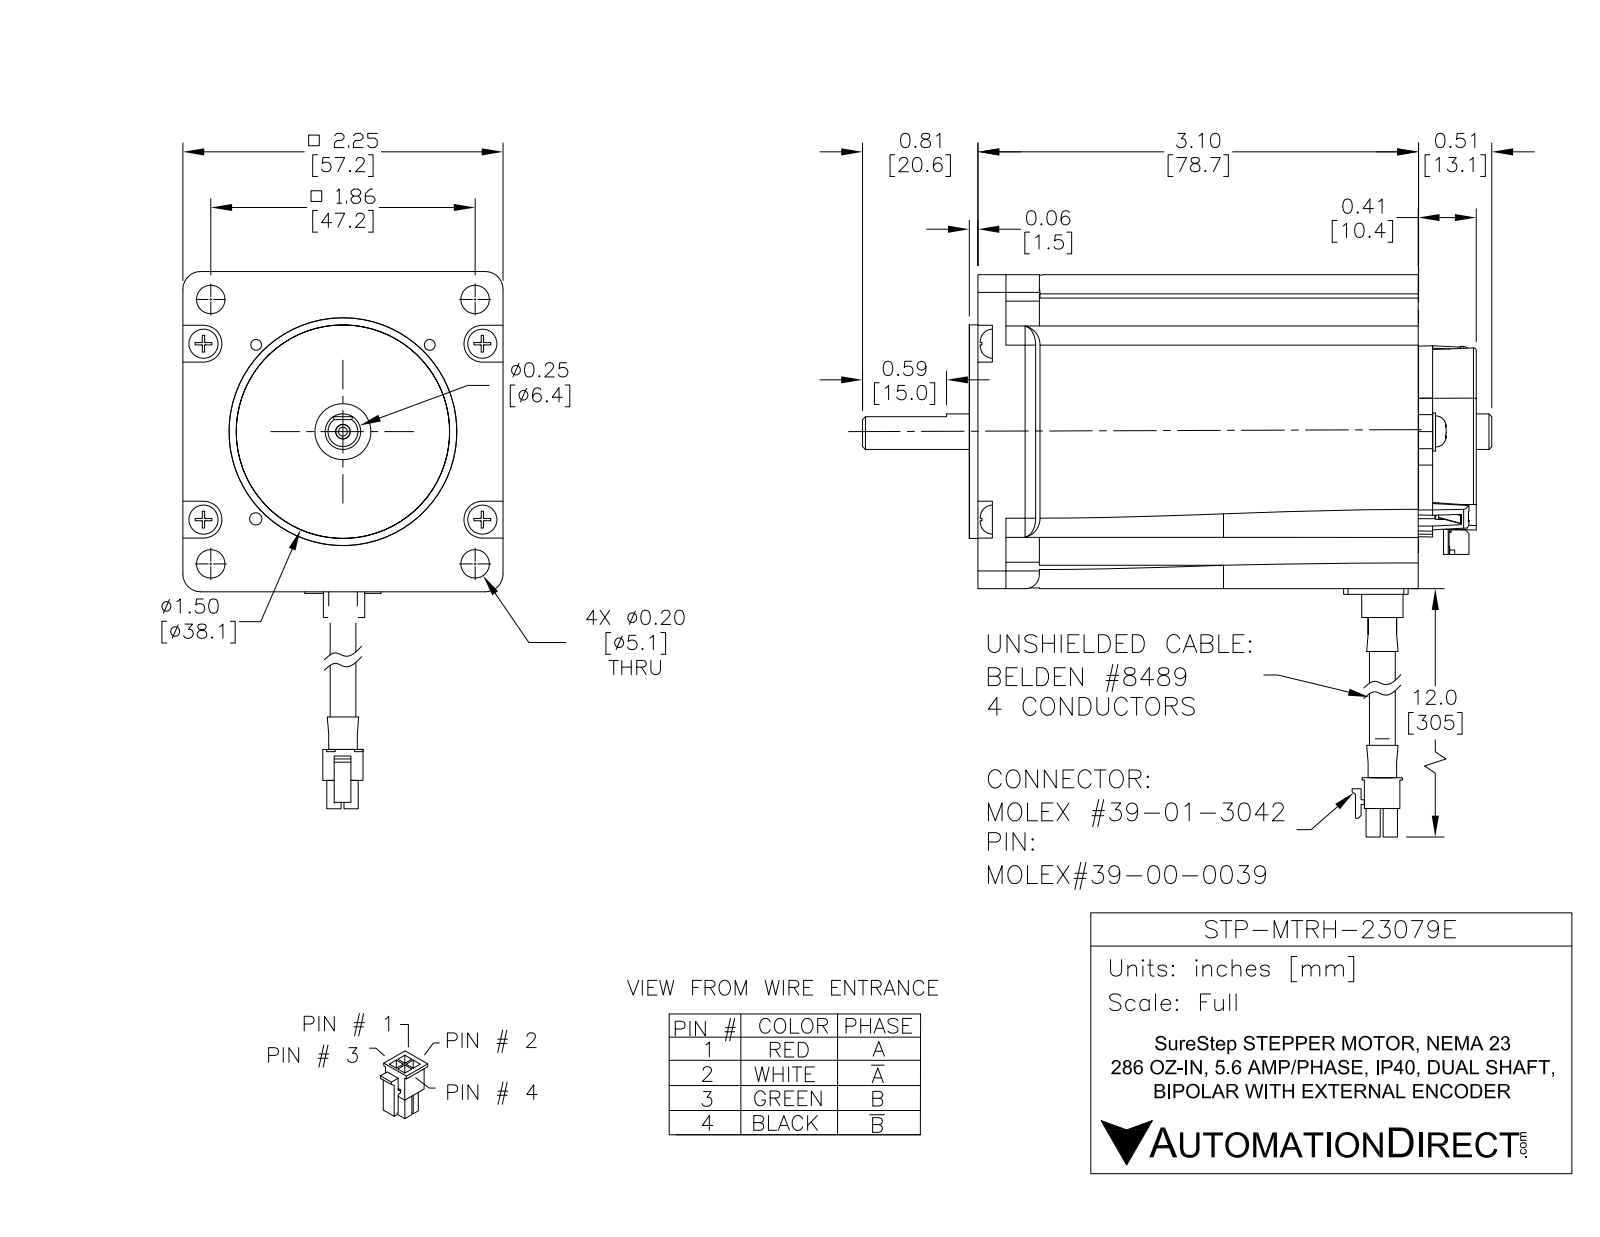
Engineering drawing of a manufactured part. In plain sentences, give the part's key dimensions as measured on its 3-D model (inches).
The part is named "STP-MTRH-23079E". Its 3-D file was written by "SolidWorks 2017 (AUTOMOTIVE_DESIGN)". It is 12 solids with 2014 faces: 1158 planar, 506 cylindrical and 350 other. Overall it measures 14.523 by 4.422 by 2.207 inches. Its volume is 13.26 cubic inches and its surface area 76.54 square inches. Round holes: 4 of diameter 0.031, 4 of diameter 0.037, 4 of diameter 0.079, 4 of diameter 0.097, 4 of diameter 0.118, 4 of diameter 0.2, 2 of diameter 0.067, 2 of diameter 0.085, 2 of diameter 0.091, 2 of diameter 0.116, 2 of diameter 0.125, 2 of diameter 0.125. Round bosses or shafts: 4 of diameter 0.059, 2 of diameter 0.268, 1 of diameter 1.7, 1 of diameter 1.5, 1 of diameter 0.465, 1 of diameter 0.413, 1 of diameter 0.29, 1 of diameter 0.217. Partial cylindrical surfaces (rounded edges, fillets, slot ends): 24 of radius 0.012, 22 of radius 0.039, 10 of radius 0.125, 6 of radius 0.02, 6 of radius 0.041, 6 of radius 0.079, 4 of radius 0.012, 4 of radius 0.016. The main face-to-face distances are 2.207, 0.314, 1.083, 1.398, 3.098, 2.014, 1.7, 1.081, 1.395, 3.095. The hole center spacings are 0.622, 1.935, 0.316, 0.707, 0.865, 1.159, 1.181, 1.314.
